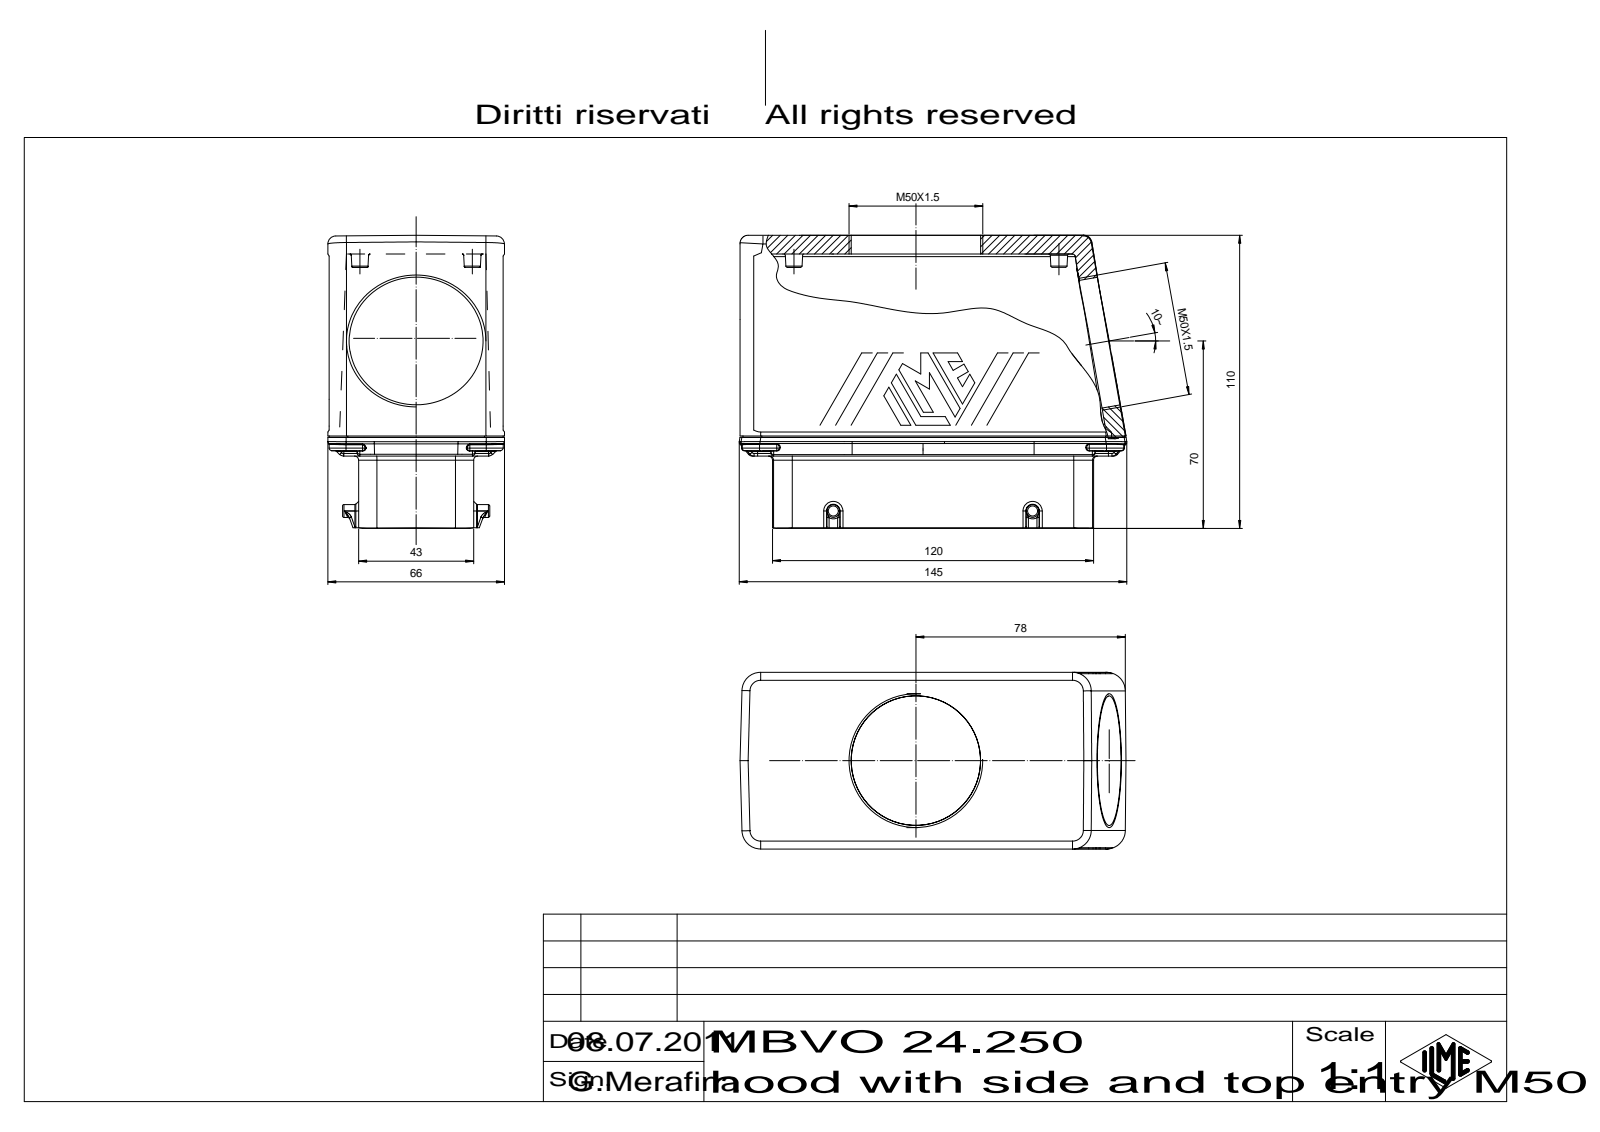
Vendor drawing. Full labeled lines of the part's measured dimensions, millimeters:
Part name (STEP PRODUCT): 53848_Body_1
STEP written by: CoCreate Modeling 16.00A 16-Aug-2008 (C) Parametric Technology GmbH (AUTOMOTIVE_DESIGN)
Units: millimetres
Bodies: 1 solid, 690 faces (374 planar, 152 cylindrical, 164 other)
Overall size (bounding box): 143.75 × 108.97 × 66.01
Volume: 639 340 mm³ · Surface area: 77 019 mm²
Round holes (diameter × count): ⌀50 ×2
Round bosses / shafts (diameter × count): ⌀4.8 ×2
Partial cylindrical surfaces — rounded edges, fillets, slot ends (radius × count): R1 ×44, R0.3 ×18, R7 ×12, R3 ×10, R0.5 ×8, R1.5 ×6, R4.2 ×4, R5 ×4
Main face-to-face distances: 65.01, 82.21, 0.4, 65.41, 11, 54.01, 54, 43, 11.01, 11.4
